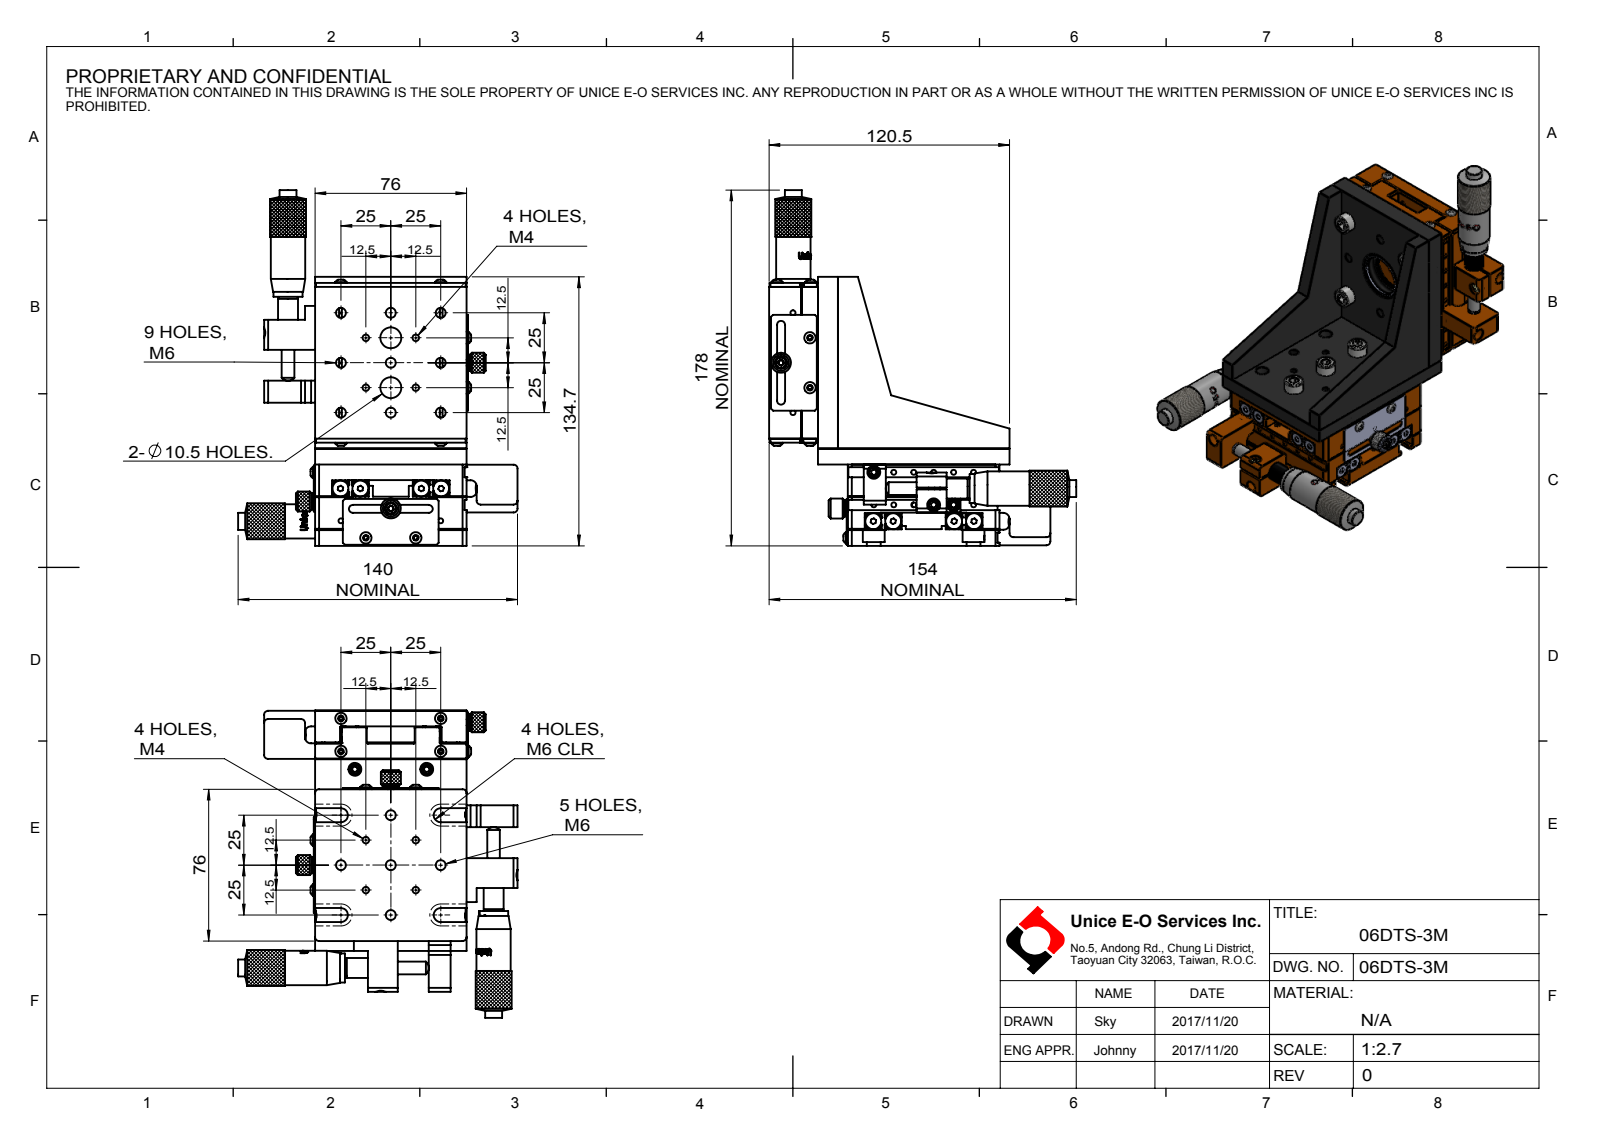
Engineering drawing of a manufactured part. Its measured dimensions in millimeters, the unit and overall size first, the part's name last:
Units: millimetres
Overall size (bounding box): 178.2 × 154 × 140
Round holes (diameter × count): ⌀2.5 ×54, ⌀5 ×14, ⌀6.5 ×14, ⌀3.3 ×8, ⌀7 ×4, ⌀6 ×3, ⌀10 ×3, ⌀10.5 ×2, ⌀6.7 ×1, ⌀14.65 ×1, ⌀22 ×1, ⌀23 ×1
Round bosses / shafts (diameter × count): ⌀5.7 ×12, ⌀8 ×11, ⌀10 ×10, ⌀18 ×3, ⌀17.2 ×3, ⌀14.6 ×3, ⌀9.75 ×3, ⌀8.5 ×3
Partial cylindrical surfaces — rounded edges, fillets, slot ends (radius × count): R0.5 ×29, R2 ×28, R3 ×6, R5.5 ×4, R8.55 ×3
Main face-to-face distances: 8, 16.4, 76, 8.5, 7.5, 8.2, 16.1, 5, 7.9, 24.5
Hole centre spacings: 10, 17.68, 20, 25, 39.53, 50, 30, 35.36
Bodies: 0 solids, 1392 faces (705 planar, 485 cylindrical, 202 other)
Part name (STEP PRODUCT): 06DTS-3M
STEP written by: SolidWorks 2016 (CONFIG_CONTROL_DESIGN)
